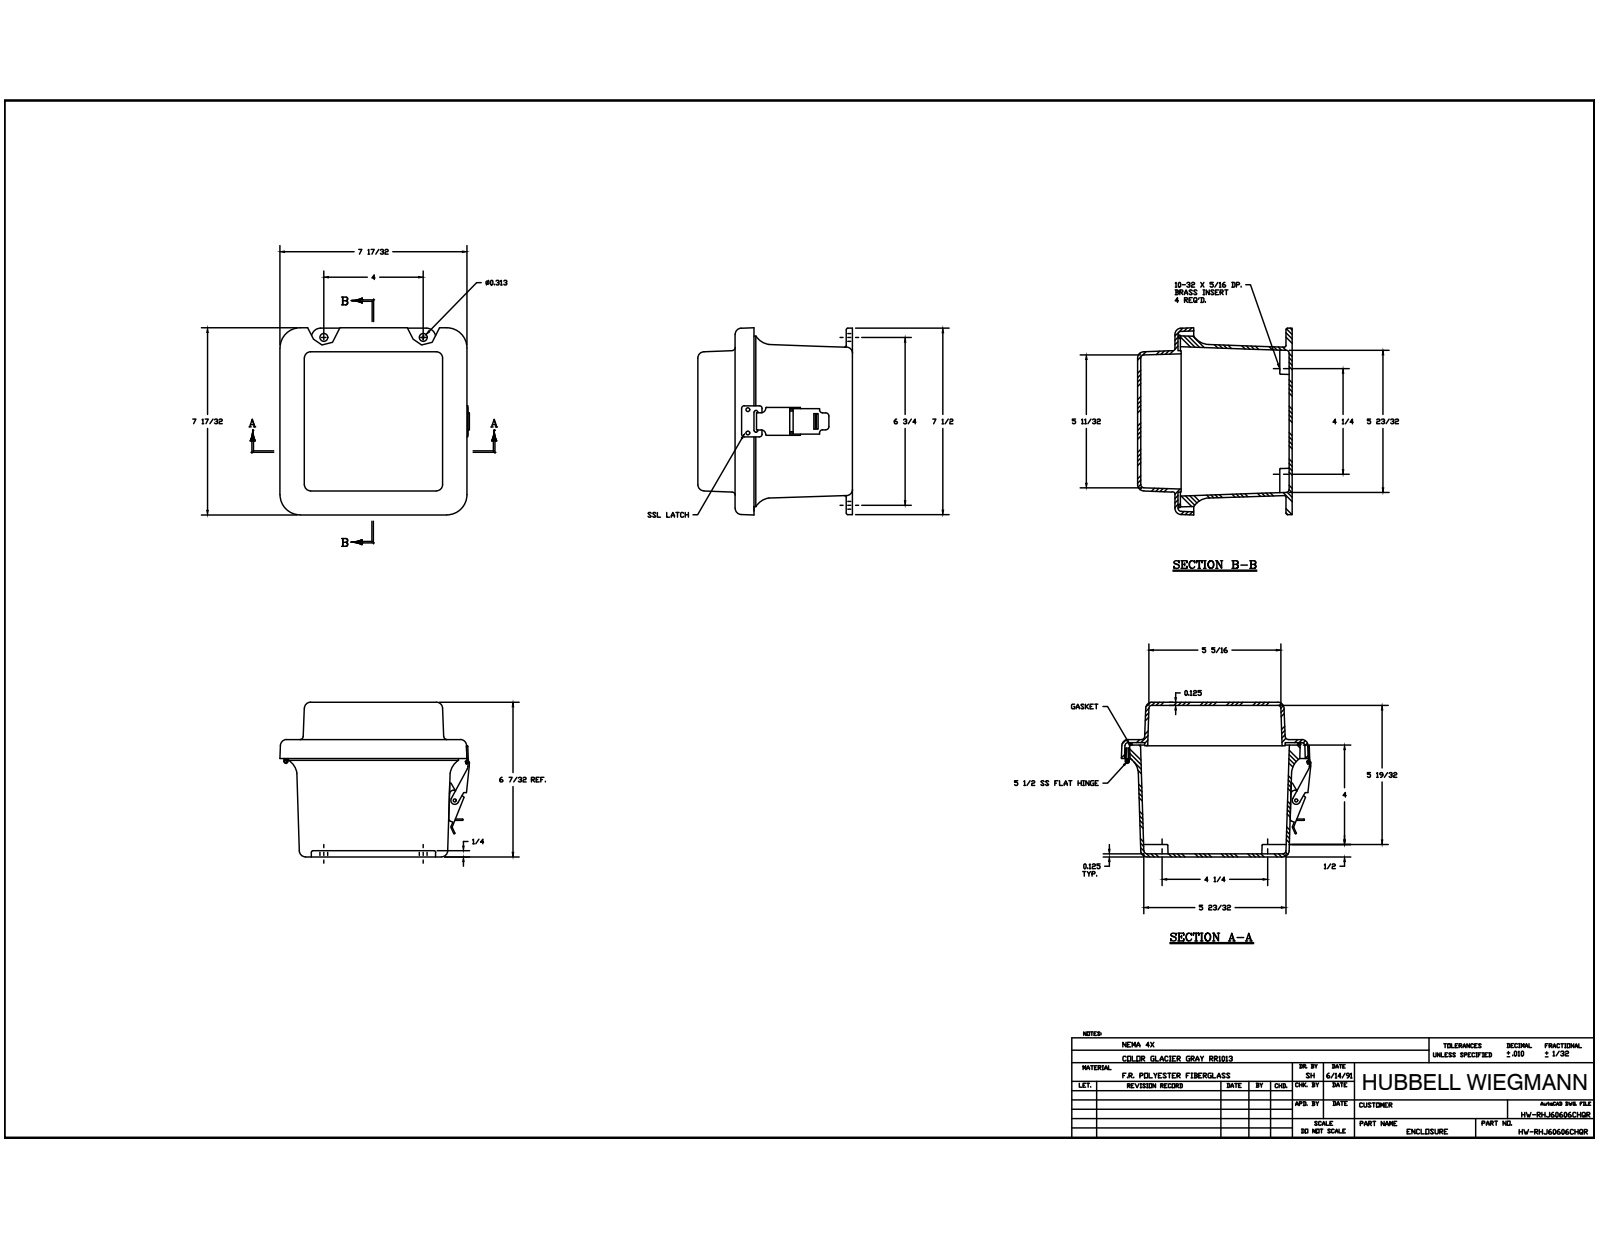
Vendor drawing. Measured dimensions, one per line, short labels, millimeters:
name: J606HL_3; RMINS45821P_111; RMINS45821P_112; RMINS45821P_113 (+8 more)
written by: Autodesk Inventor 2014 (AUTOMOTIVE_DESIGN)
unit: mm
bodies: 25 solids, 698 faces (272 planar, 278 cylindrical, 148 other)
size: 193.41 × 191.13 × 160.99
volume: 664 994 mm³; area: 374 580 mm²
holes: 11× ⌀3.56, 5× ⌀3.33, 5× ⌀3.86, 4× ⌀2.64, 4× ⌀3.96, 4× ⌀5.54, 2× ⌀3.3, 2× ⌀3.43, 1× ⌀2.16, 1× ⌀9.52
bosses: 9× ⌀3.17, 5× ⌀6.35, 4× ⌀6.86, 1× ⌀7.62, 1× ⌀4.31, 1× ⌀3.94, 1× ⌀3.05
rounds: 20× R0.79, 20× R3.17, 16× R6.35, 12× R0.38, 8× R1.14, 6× R0.76, 5× R0.57, 4× R1.52
face distances: 3.18, 3.17, 38.1, 116.54, 154.64, 157.81, 160.99, 157.82, 119.71, 41.28
hole spacings: 134.82, 23.81, 34.8, 63.5, 107.94, 157.16, 187.45, 19.05
